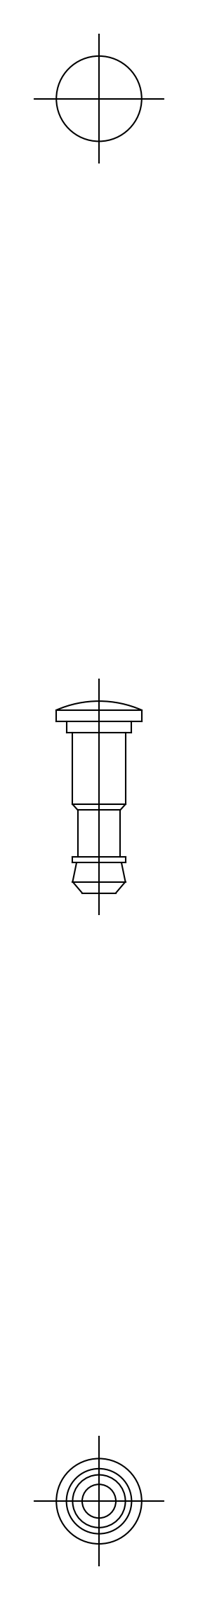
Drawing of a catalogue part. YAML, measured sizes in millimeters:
part_name: "plunger"
step_written_by: "CADfix (AUTOMOTIVE_DESIGN)"
units: millimeters
bodies: {solids: 1, faces: 22, planar: 0, cylindrical: 0, other: 22}
overall_size: [17.1, 7.6, 7.6]
volume: 302
surface_area: 336
